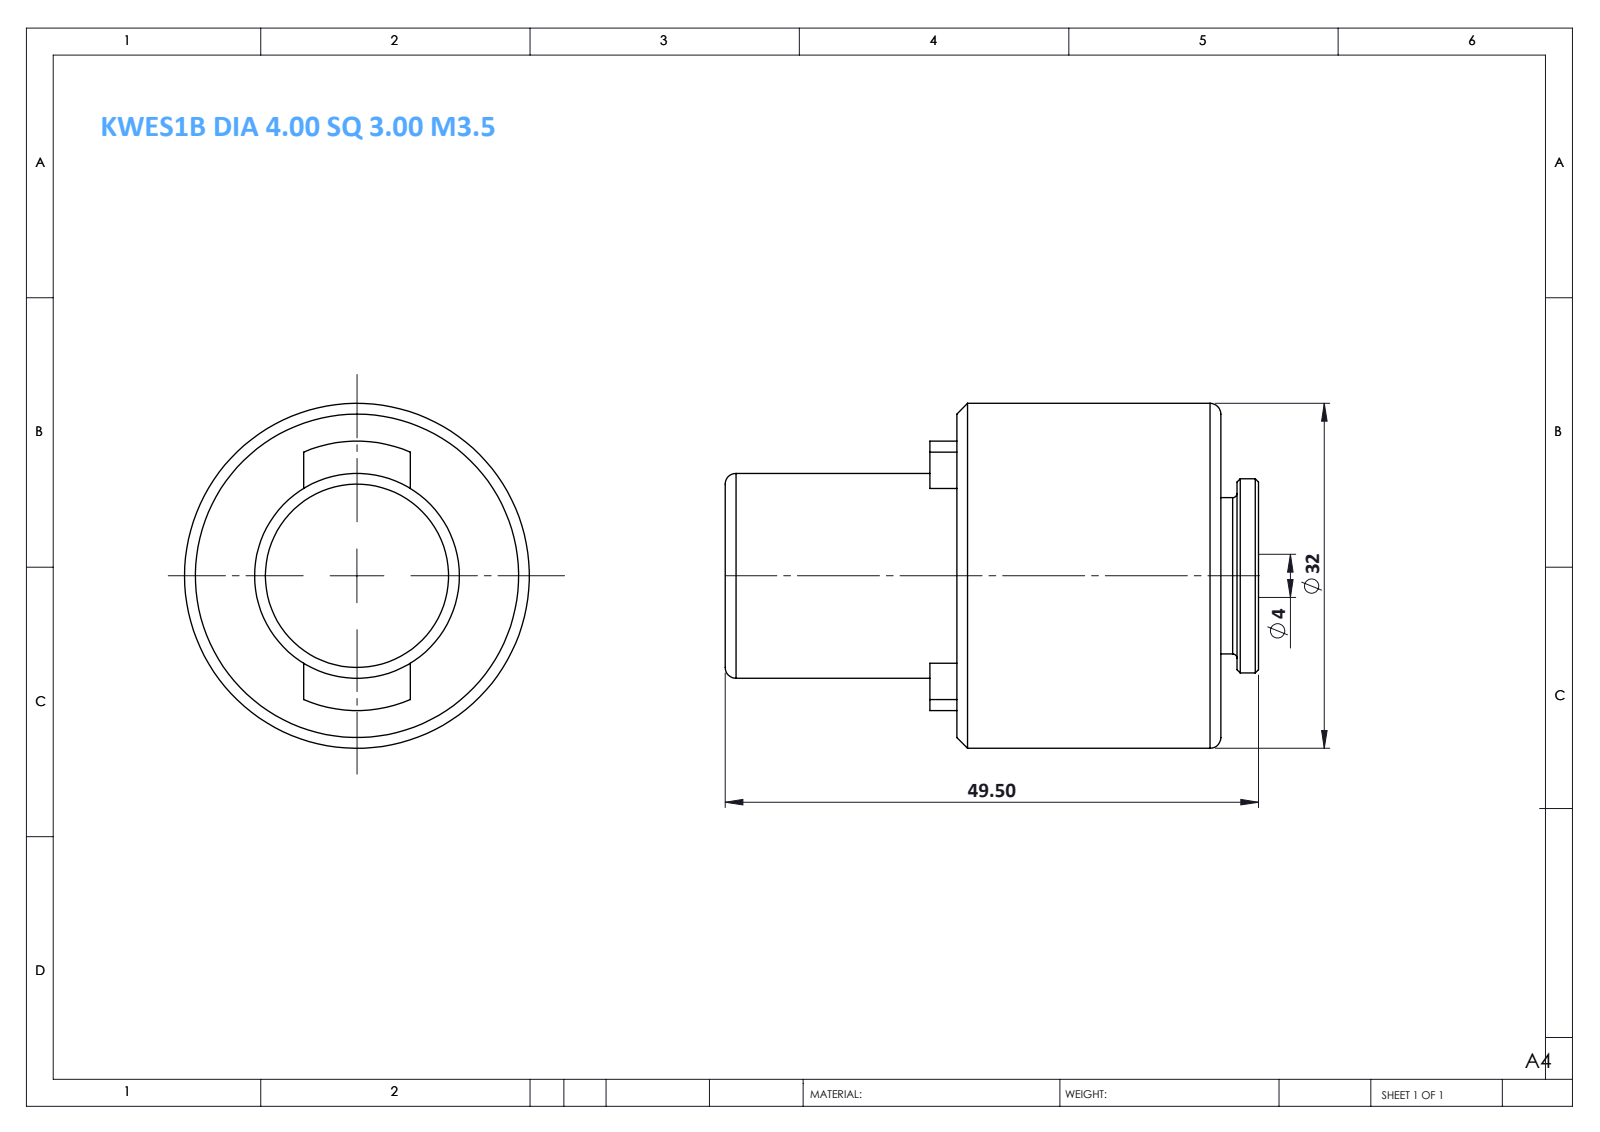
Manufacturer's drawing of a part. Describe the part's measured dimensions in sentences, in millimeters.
The part is named "KWES1B DIA 4.00 SQ 3.00 7-32'''''''' UNC". Its 3-D file was written by "SolidWorks 2014 (CONFIG_CONTROL_DESIGN)". It is 1 solid with 39 faces: 12 planar, 13 cylindrical and 14 other. Overall it measures 49.5 by 32 by 32 millimeters. Its volume is 26 447 cubic millimeters and its surface area 5 762 square millimeters. Round holes: 1 of diameter 4. Round bosses or shafts: 1 of diameter 32, 1 of diameter 19, 1 of diameter 18, 1 of diameter 14.5. Partial cylindrical surfaces (rounded edges, fillets, slot ends): 1 of radius 12.5. The main face-to-face distances are 24.5, 21.5, 46, 49.5, 28, 3.5, 19, 2.5, 27, 30.5.
